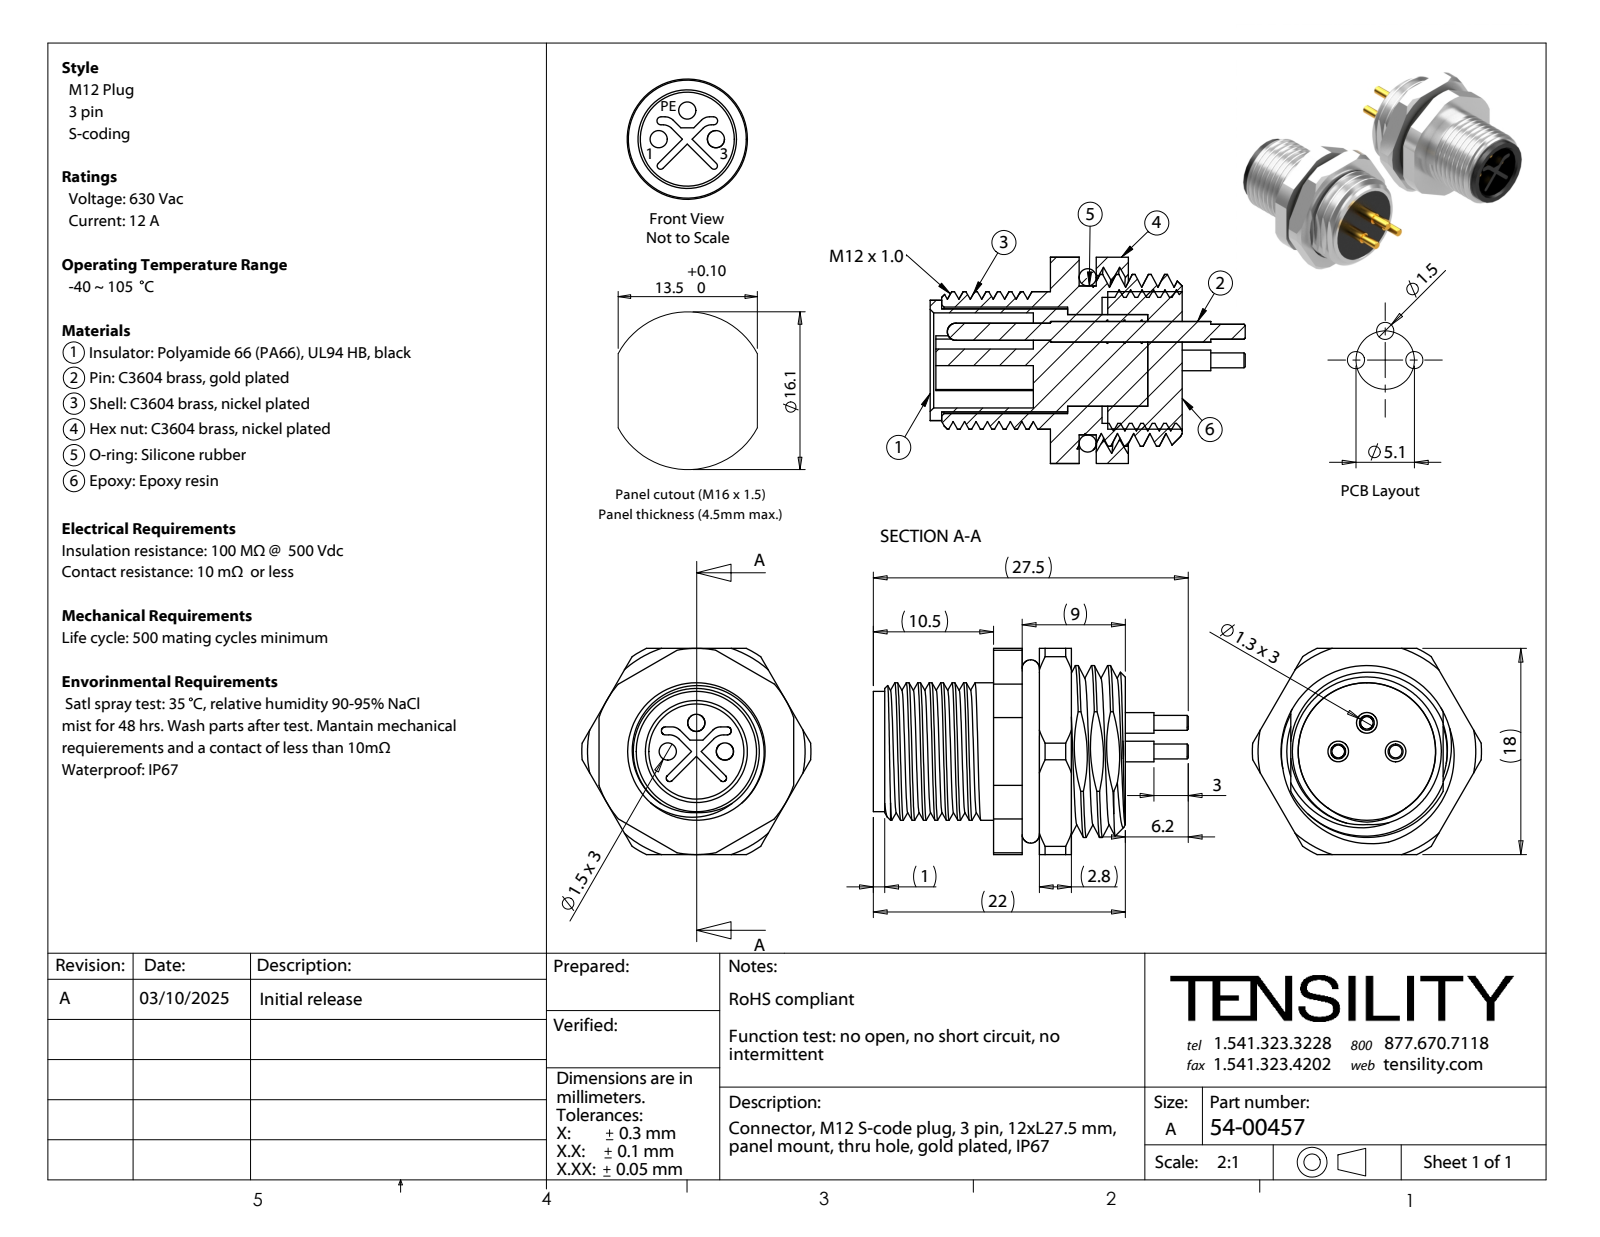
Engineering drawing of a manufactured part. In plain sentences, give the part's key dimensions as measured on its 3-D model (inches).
The part is named "54-00457-04; 54-00457-05; 54-00457; 54-00457-01 (+2 more)". Its 3-D file was written by "SolidWorks 2021 (CONFIG_CONTROL_DESIGN)". It is 8 solids with 303 faces: 80 planar, 141 cylindrical and 82 other. Overall it measures 1.083 by 0.787 by 0.709 inches. Its volume is 0.185 cubic inches and its surface area 8.843 square inches. Round holes: 3 of diameter 0.059, 1 of diameter 0.315, 1 of diameter 0.327, 1 of diameter 0.366, 1 of diameter 0.433, 1 of diameter 0.551. Round bosses or shafts: 3 of diameter 0.071, 3 of diameter 0.051, 1 of diameter 0.512, 1 of diameter 0.472, 1 of diameter 0.413, 1 of diameter 0.354. Partial cylindrical surfaces (rounded edges, fillets, slot ends): 2 of radius 0.012, 2 of radius 0.014, 2 of radius 0.039, 2 of radius 0.05, 1 of radius 0.295, 1 of radius 0.354, 1 of radius 0.394. The main face-to-face distances are 0.098, 0.157, 0.059, 0.118, 0.453, 0.354, 0.177, 0.236, 0.039, 0.709. The hole center spacings are 0.098, 0.139, 0.197.
